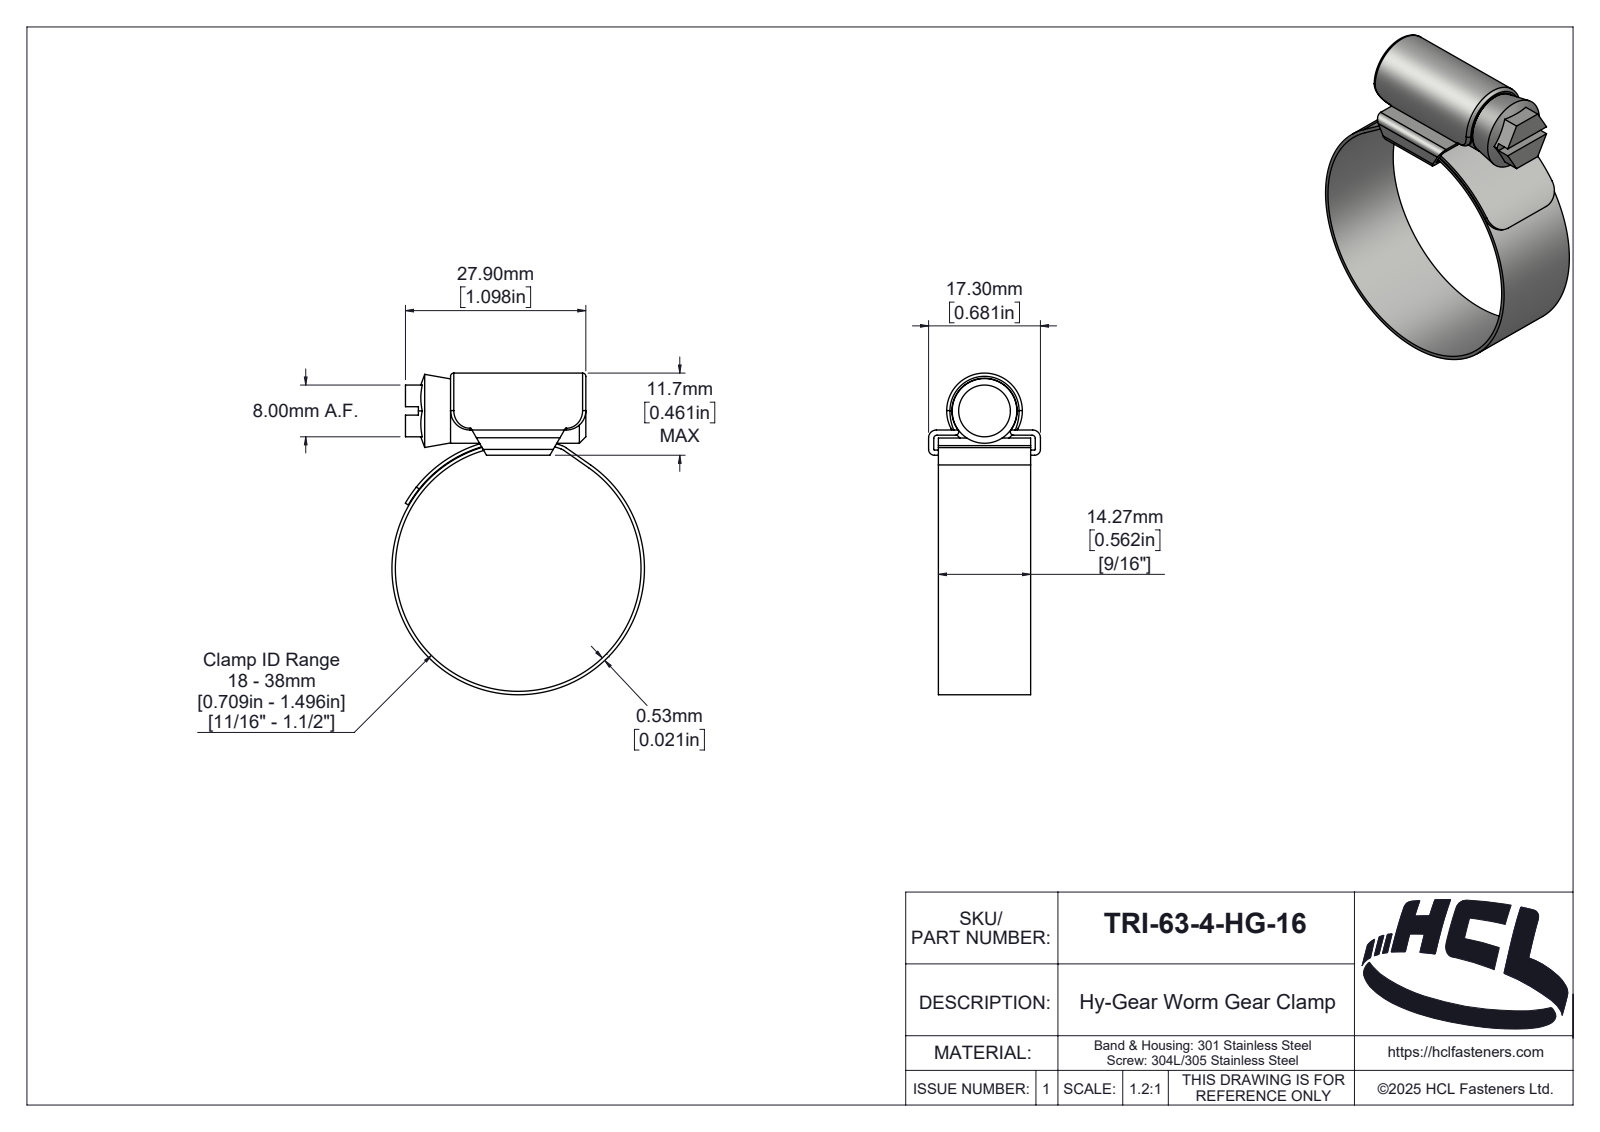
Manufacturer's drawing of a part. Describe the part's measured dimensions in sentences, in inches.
The part is named "TRI-50-0-HG-16". Its 3-D file was written by "SolidWorks 2025 (AUTOMOTIVE_DESIGN)". It is 3 solids with 189 faces: 39 planar, 89 cylindrical and 61 other. Overall it measures 1.958 by 1.538 by 0.681 inches. Its volume is 0.236 cubic inches and its surface area 10.86 square inches. Round holes: 1 of diameter 1.496. Round bosses or shafts: 1 of diameter 1.538, 1 of diameter 0.394. Partial cylindrical surfaces (rounded edges, fillets, slot ends): 6 of radius 0.02, 4 of radius 0.118, 2 of radius 0.004, 2 of radius 0.035, 2 of radius 0.047, 1 of radius 0.018, 1 of radius 0.074, 1 of radius 0.079. The main face-to-face distances are 0.031, 0.122, 0.091, 0.561, 0.154, 0.021, 1.098, 0.06, 0.621, 0.65.
